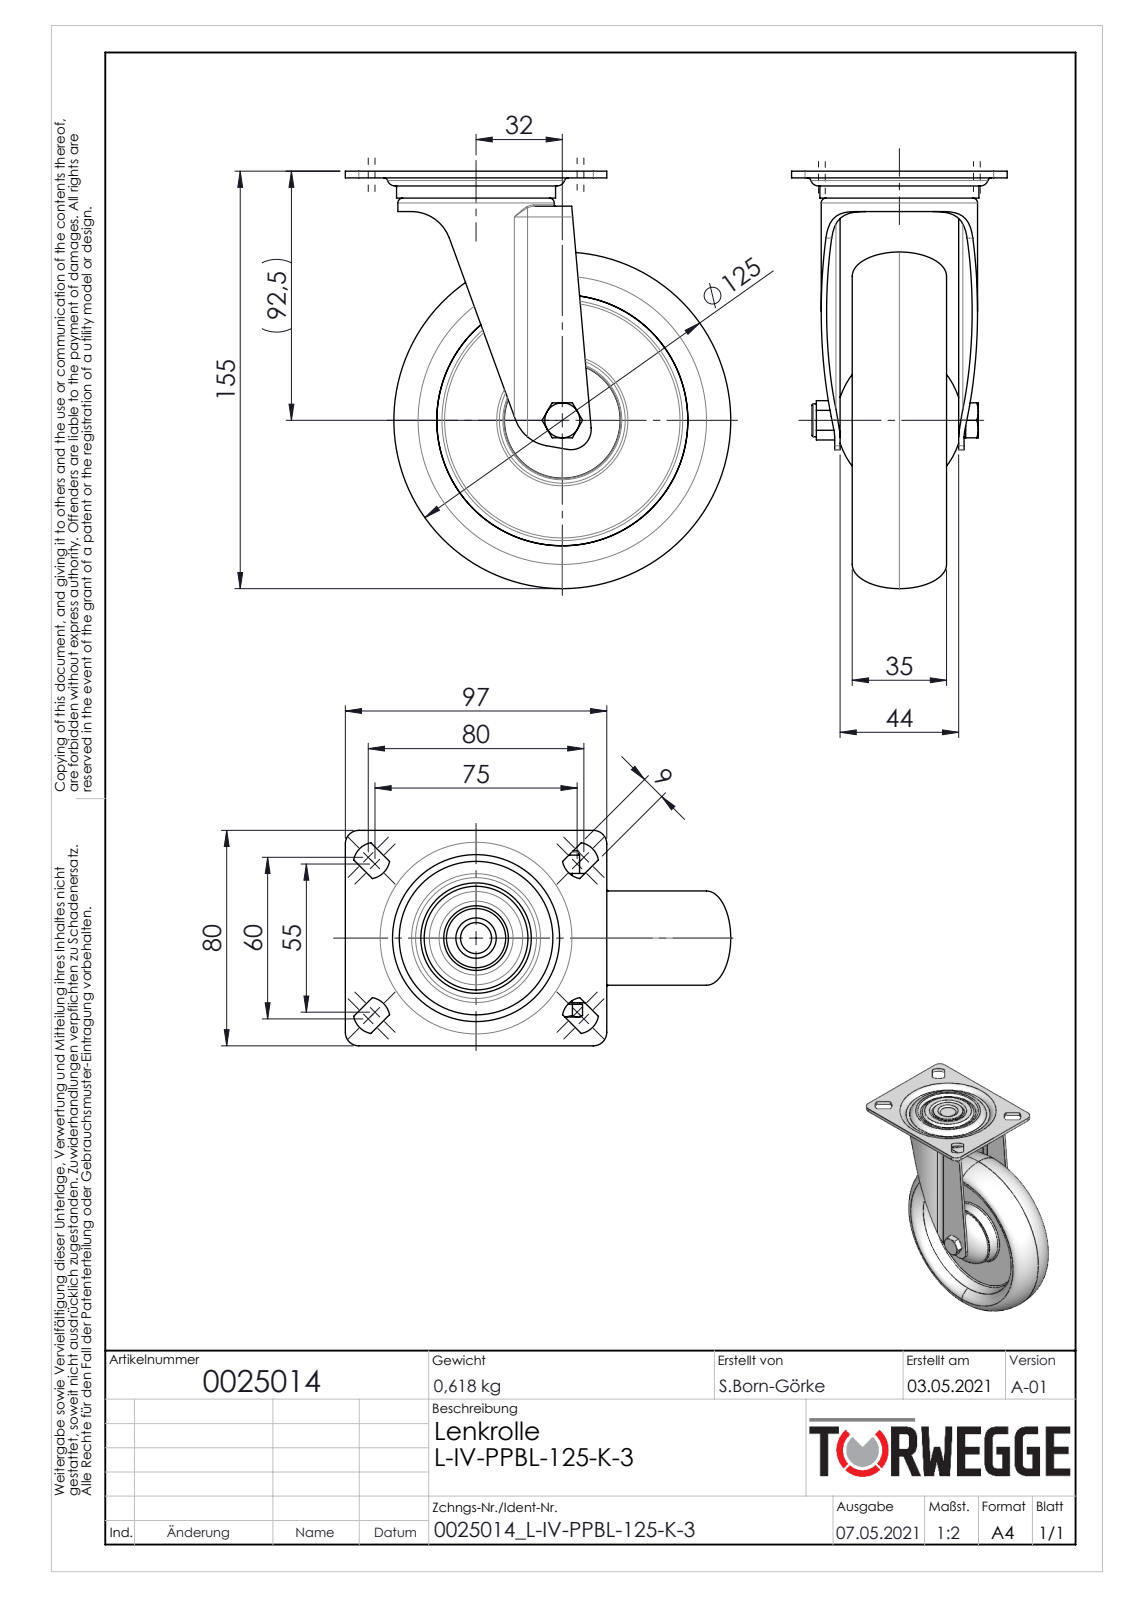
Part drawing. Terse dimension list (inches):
name: 0025014
written by: SolidWorks 2020 (AUTOMOTIVE_DESIGN)
unit: in
bodies: 7 solids, 248 faces (76 planar, 64 cylindrical, 108 other)
size: 6.102 × 5.63 × 3.15
volume: 17.85 in³; area: 190 in²
holes: 1× ⌀0.262, 1× ⌀0.315, 1× ⌀0.323, 1× ⌀1.299, 1× ⌀1.378, 1× ⌀2.126
bosses: 1× ⌀2.323, 1× ⌀2.283, 1× ⌀1.142, 1× ⌀0.866, 1× ⌀0.591, 1× ⌀0.512, 1× ⌀0.48
rounds: 8× R0.318, 4× R0.197, 2× R0.079, 2× R0.157, 2× R0.394, 2× R0.472, 2× R0.591, 1× R0.295
face distances: 0.197, 0.079, 0.098, 0.846, 0.768, 0.965, 1.043, 1.811, 0.472, 0.522
